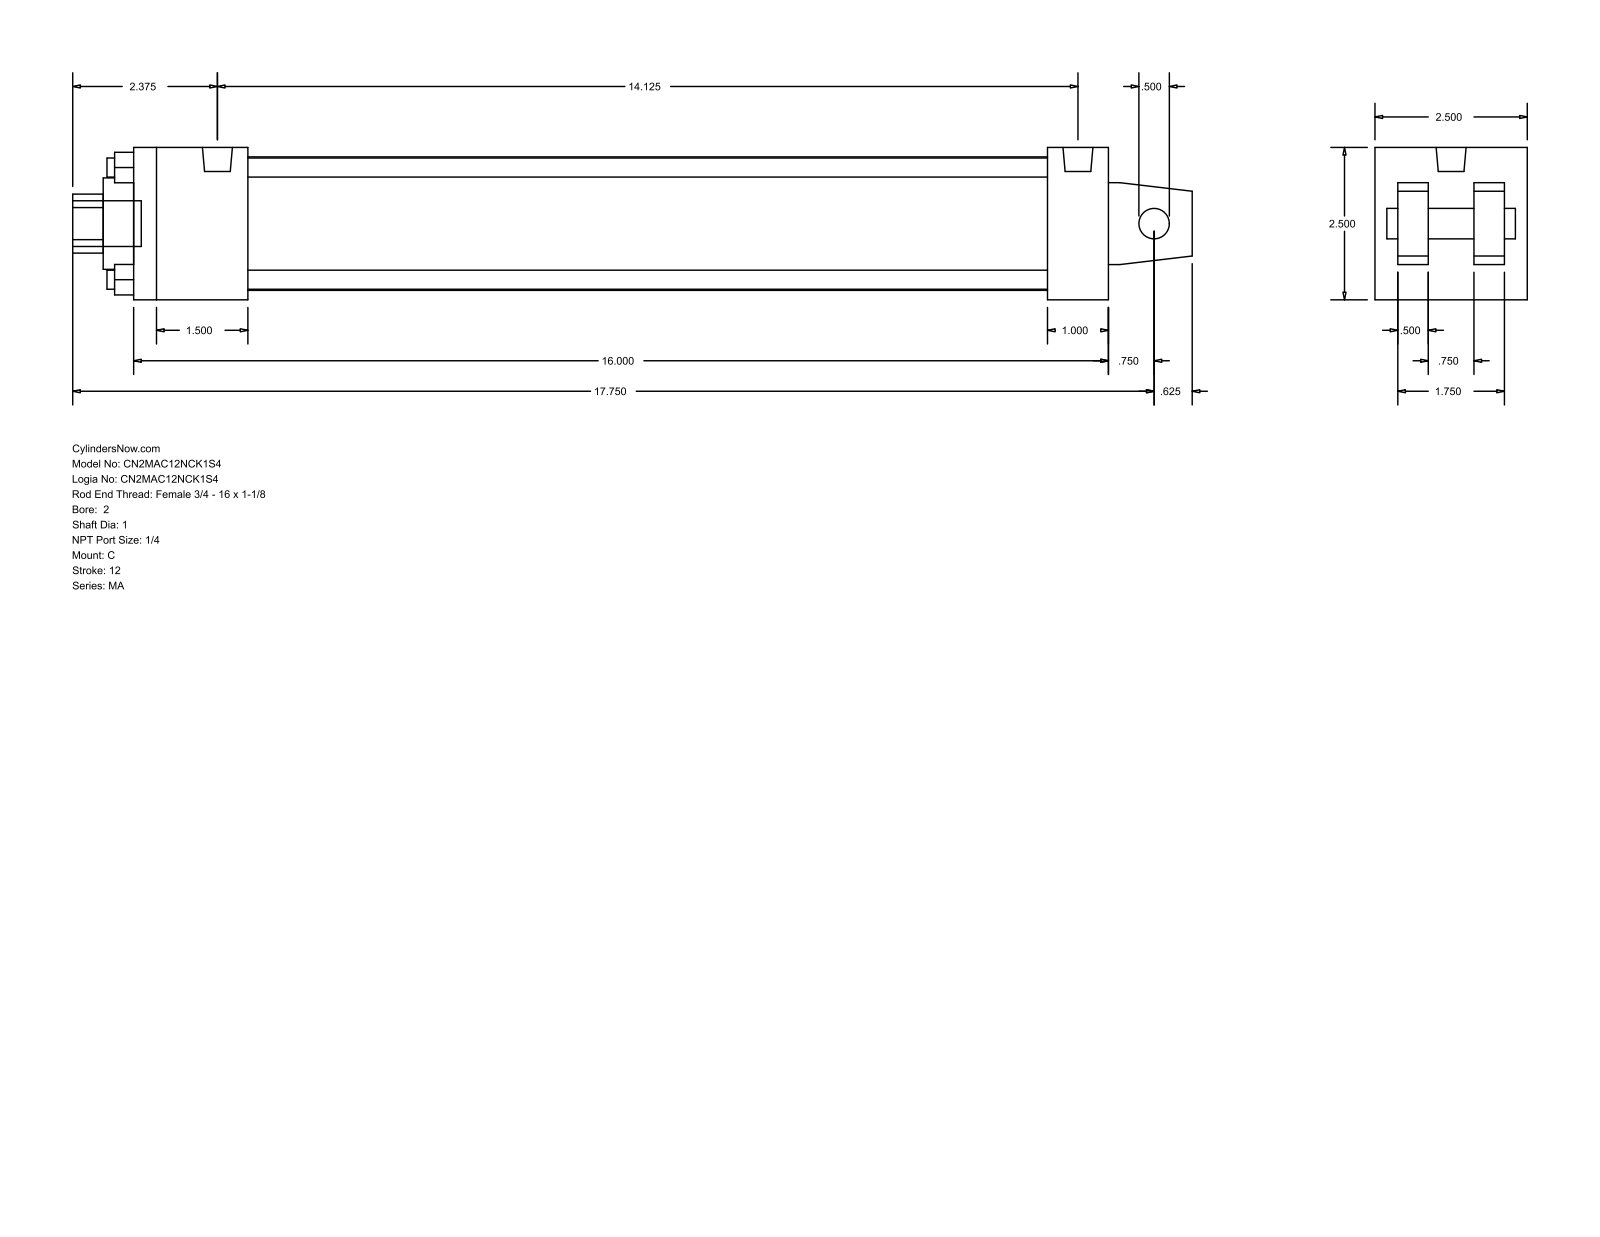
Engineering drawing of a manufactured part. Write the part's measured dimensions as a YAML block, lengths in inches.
part_name: "MA_C__0200_1"
step_written_by: "GSSL Pune (CONFIG_CONTROL_DESIGN)"
units: inches
bodies: {solids: 0, faces: 103, planar: 76, cylindrical: 27, other: 0}
overall_size: [18.375, 2.5, 2.5]
round_holes:
  - {diameter: 0.313, count: 4}
  - {diameter: 0.5, count: 1}
  - {diameter: 1, count: 1}
  - {diameter: 1.5, count: 1}
  - {diameter: 2.19, count: 1}
round_bosses_or_shafts:
  - {diameter: 0.313, count: 4}
  - {diameter: 0.492, count: 2}
  - {diameter: 0.75, count: 1}
partial_cylinders:
  - {radius: 0.484, count: 1}
face_to_face_distances: [2.5, 0.5, 16, 0.875, 1.625, 0.375, 2.125, 1.25, 1.875, 1]
hole_center_spacings: [1.301, 1.84, 2.602]
